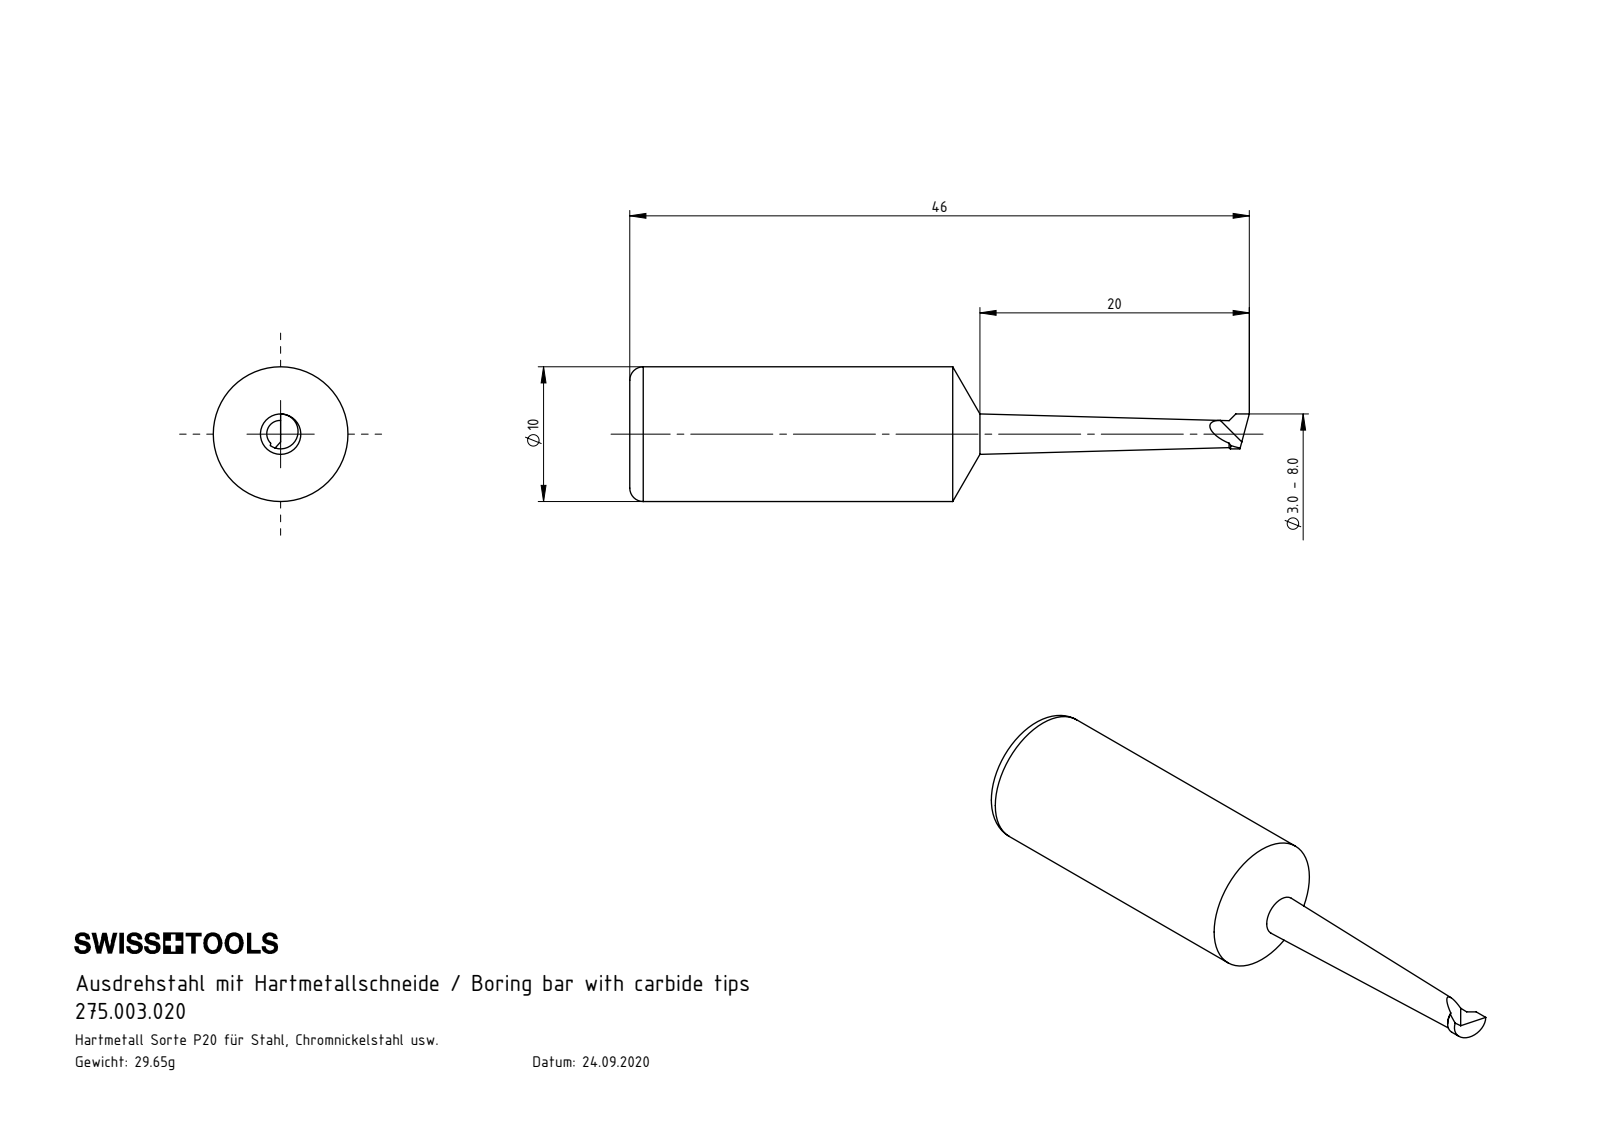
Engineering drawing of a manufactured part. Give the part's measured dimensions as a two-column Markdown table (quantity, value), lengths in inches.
| quantity | value |
| --- | --- |
| part name | 275.003.020 |
| STEP written by | SolidWorks 2022 (AUTOMOTIVE_DESIGN) |
| units | inches |
| bodies | 1 solid, 14 faces (4 planar, 3 cylindrical, 7 other) |
| overall size | 1.811 × 0.394 × 0.394 |
| volume | 0.125 in³ |
| surface area | 1.638 in² |
| round bosses / shafts (diameter × count) | 0.394 × 1 |
| partial cylindrical surfaces (radius × count) | 0.051 × 1 |
